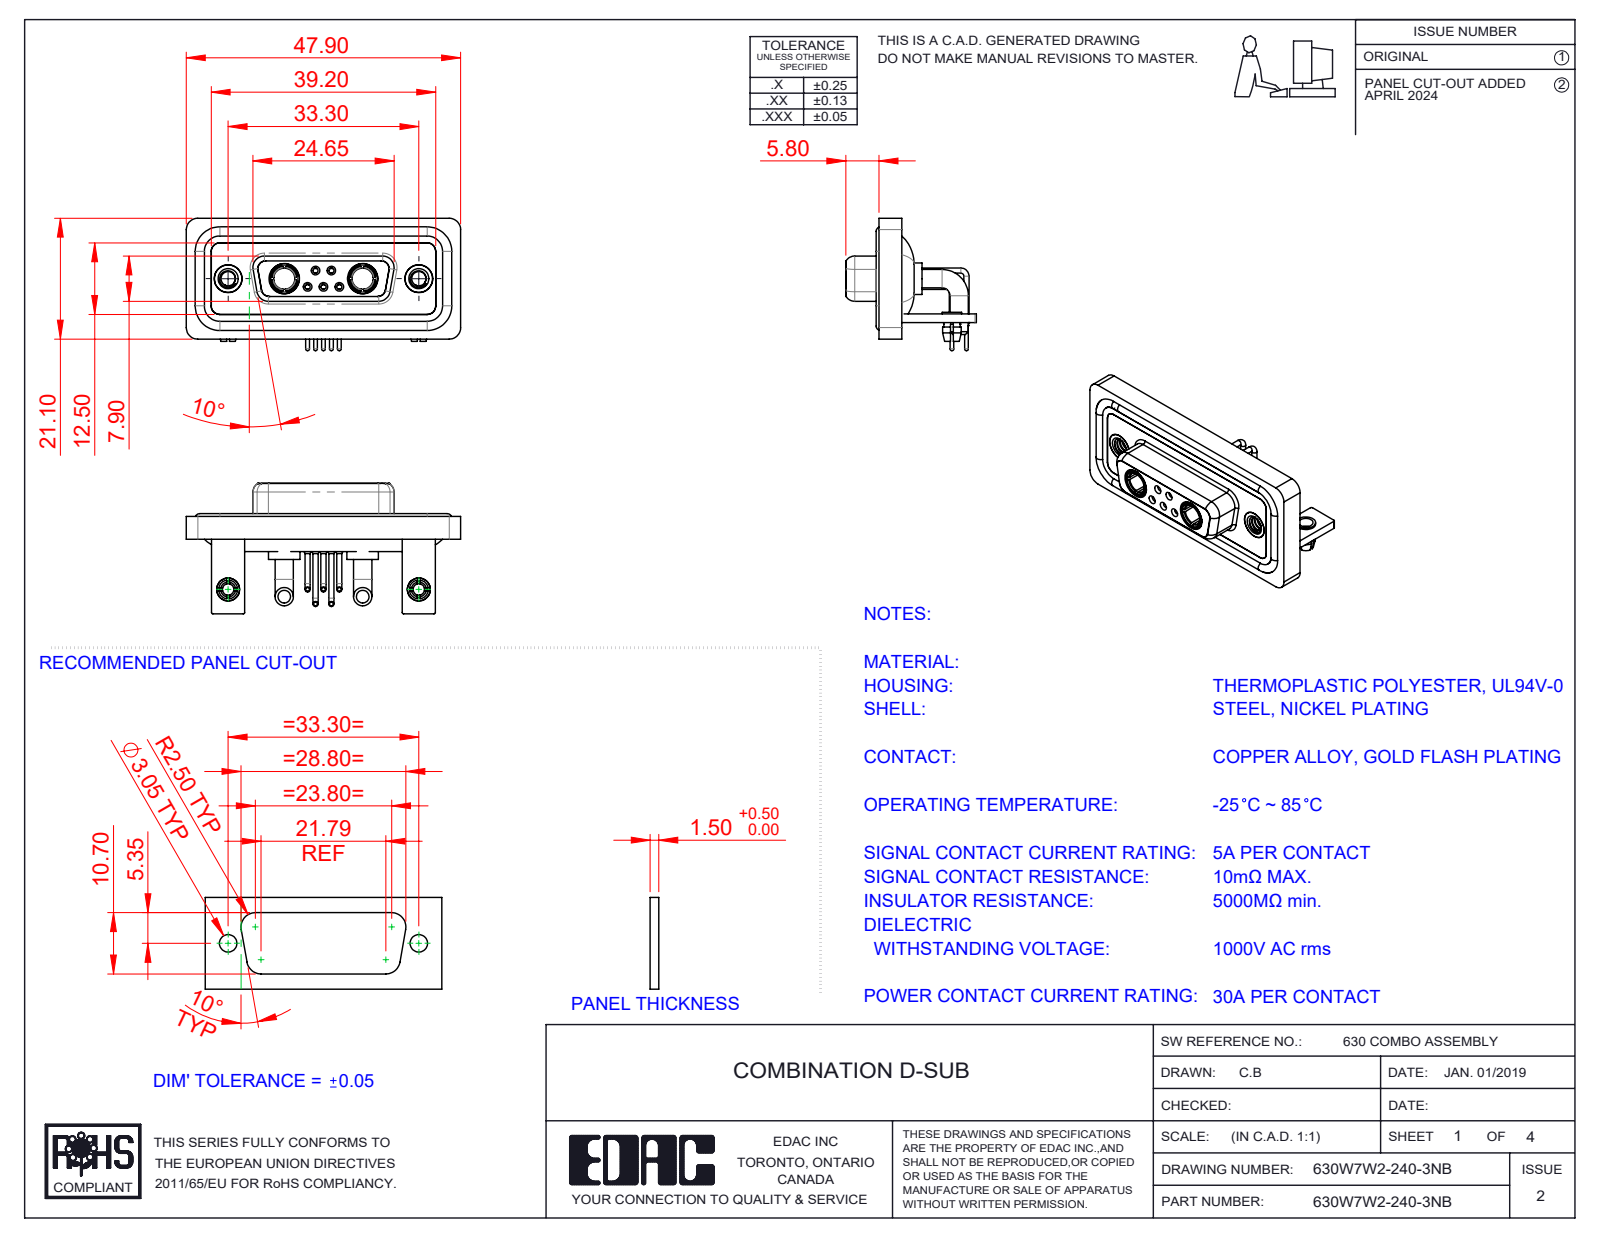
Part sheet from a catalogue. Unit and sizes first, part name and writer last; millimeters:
Units: millimetres
Overall size (bounding box): 47.9 × 23.12 × 22.8
Round holes (diameter × count): ⌀2 ×7, ⌀0.9 ×5, ⌀1.1 ×5, ⌀1.5 ×5, ⌀2.5 ×4, ⌀4.85 ×4, ⌀1.6 ×3, ⌀1.7 ×2, ⌀3.2 ×2, ⌀3.7 ×2, ⌀4 ×2, ⌀4.05 ×2
Round bosses / shafts (diameter × count): ⌀1.6 ×6, ⌀0.9 ×5, ⌀0.65 ×5, ⌀3.2 ×4, ⌀5.5 ×2, ⌀5.2 ×2, ⌀4.96 ×2, ⌀4.95 ×2
Partial cylindrical surfaces — rounded edges, fillets, slot ends (radius × count): R2 ×21, R1.5 ×18, R0.25 ×16, R1.35 ×12, R1.6 ×8, R0.5 ×5, R0.6 ×4, R0.65 ×4
Main face-to-face distances: 0.4, 2.9, 1.5, 1.8, 3.7, 1.1, 4.1, 1.6, 2.5, 1.4
Hole centre spacings: 3.16, 2.77, 9.8, 23.5, 33.3, 4.31, 4.33, 5.03
Volume: 6 648 mm³ · Surface area: 11 191 mm²
Bodies: 20 solids, 941 faces (306 planar, 407 cylindrical, 228 other)
Part name (STEP PRODUCT): 630Combo Contact Row 2_50 Contacts; 630W7W2-240-3NB; 630Combo Threaded Rivet_A; 630Combo Board Lock_50 Contacts (+7 more)
STEP written by: SolidWorks 2023 (CONFIG_CONTROL_DESIGN)
